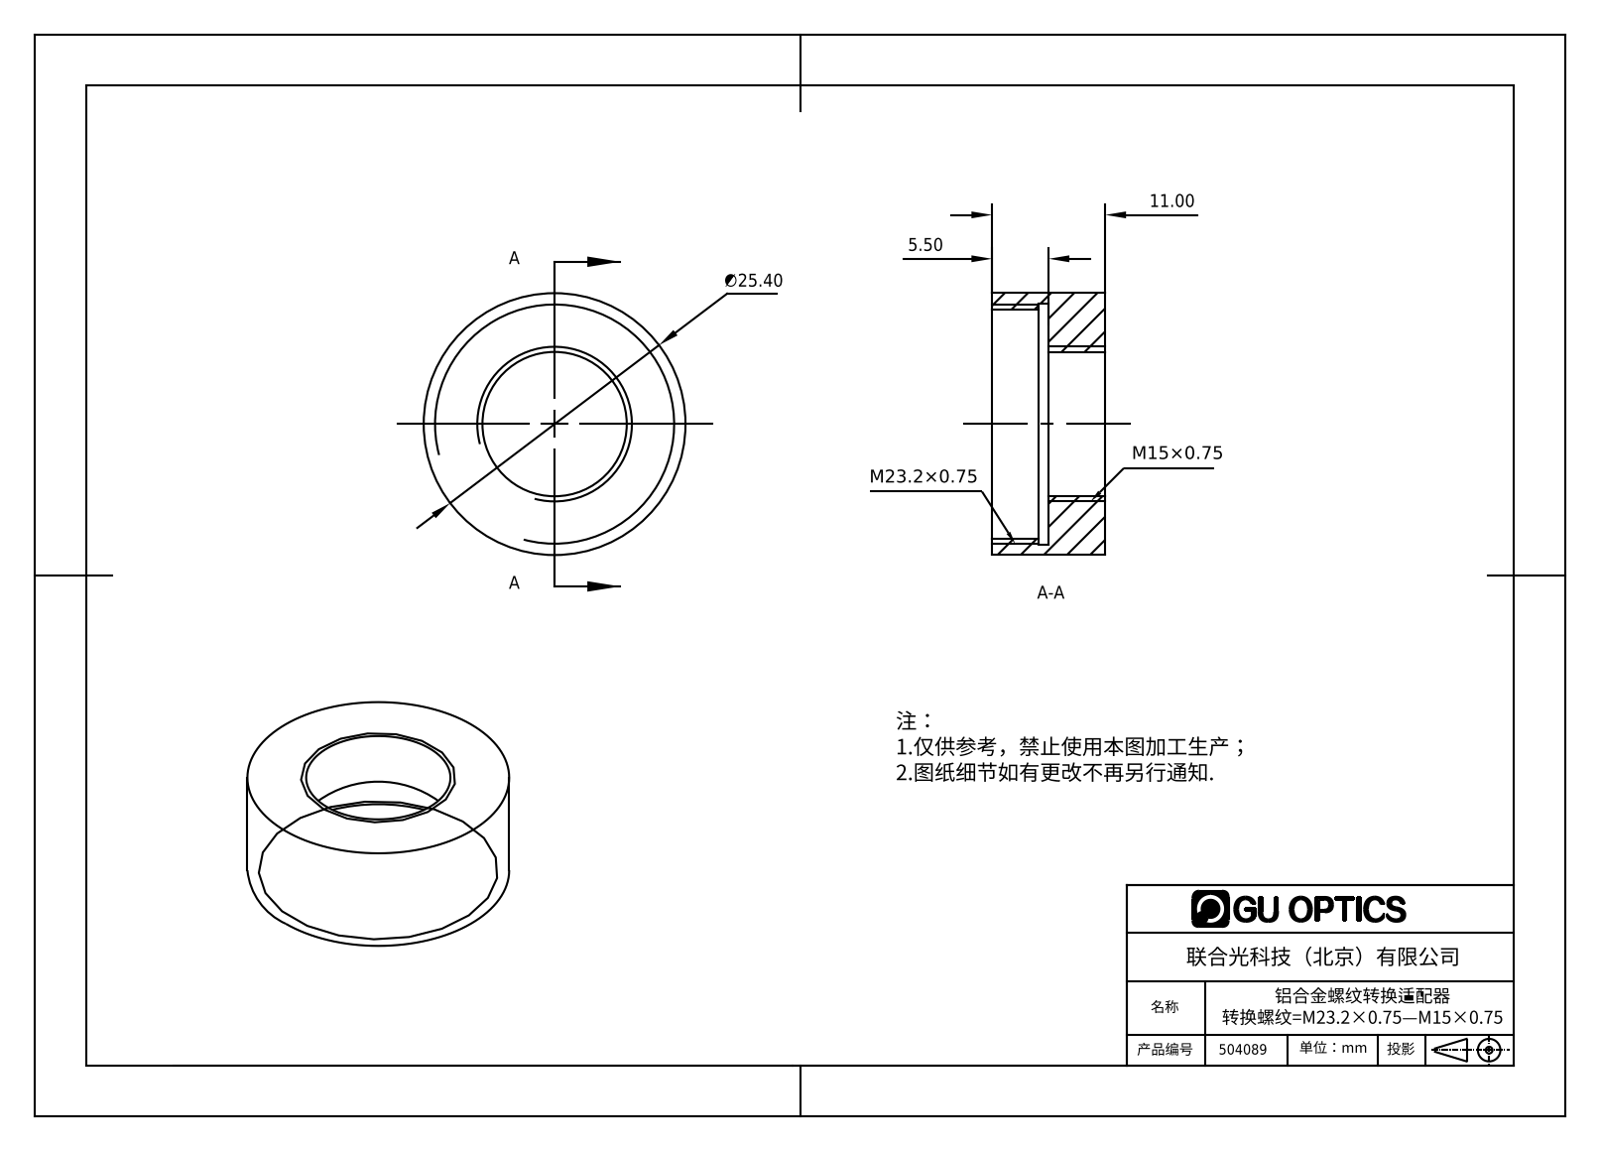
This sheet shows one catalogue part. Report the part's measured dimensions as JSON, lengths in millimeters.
{"part_name": "504089", "step_written_by": "SolidWorks 2016 (AUTOMOTIVE_DESIGN)", "units": "millimeters", "bodies": {"solids": 1, "faces": 12, "planar": 4, "cylindrical": 8, "other": 0}, "overall_size": [25.4, 25.4, 11], "volume_mm3": 2555, "surface_area_mm2": 2299, "round_holes": [[14, 1], [22.2, 1], [23.4, 1]], "round_bosses_or_shafts": [[25.4, 1]], "face_to_face_distances": [5.5, 11, 4.5, 1, 6.5]}
